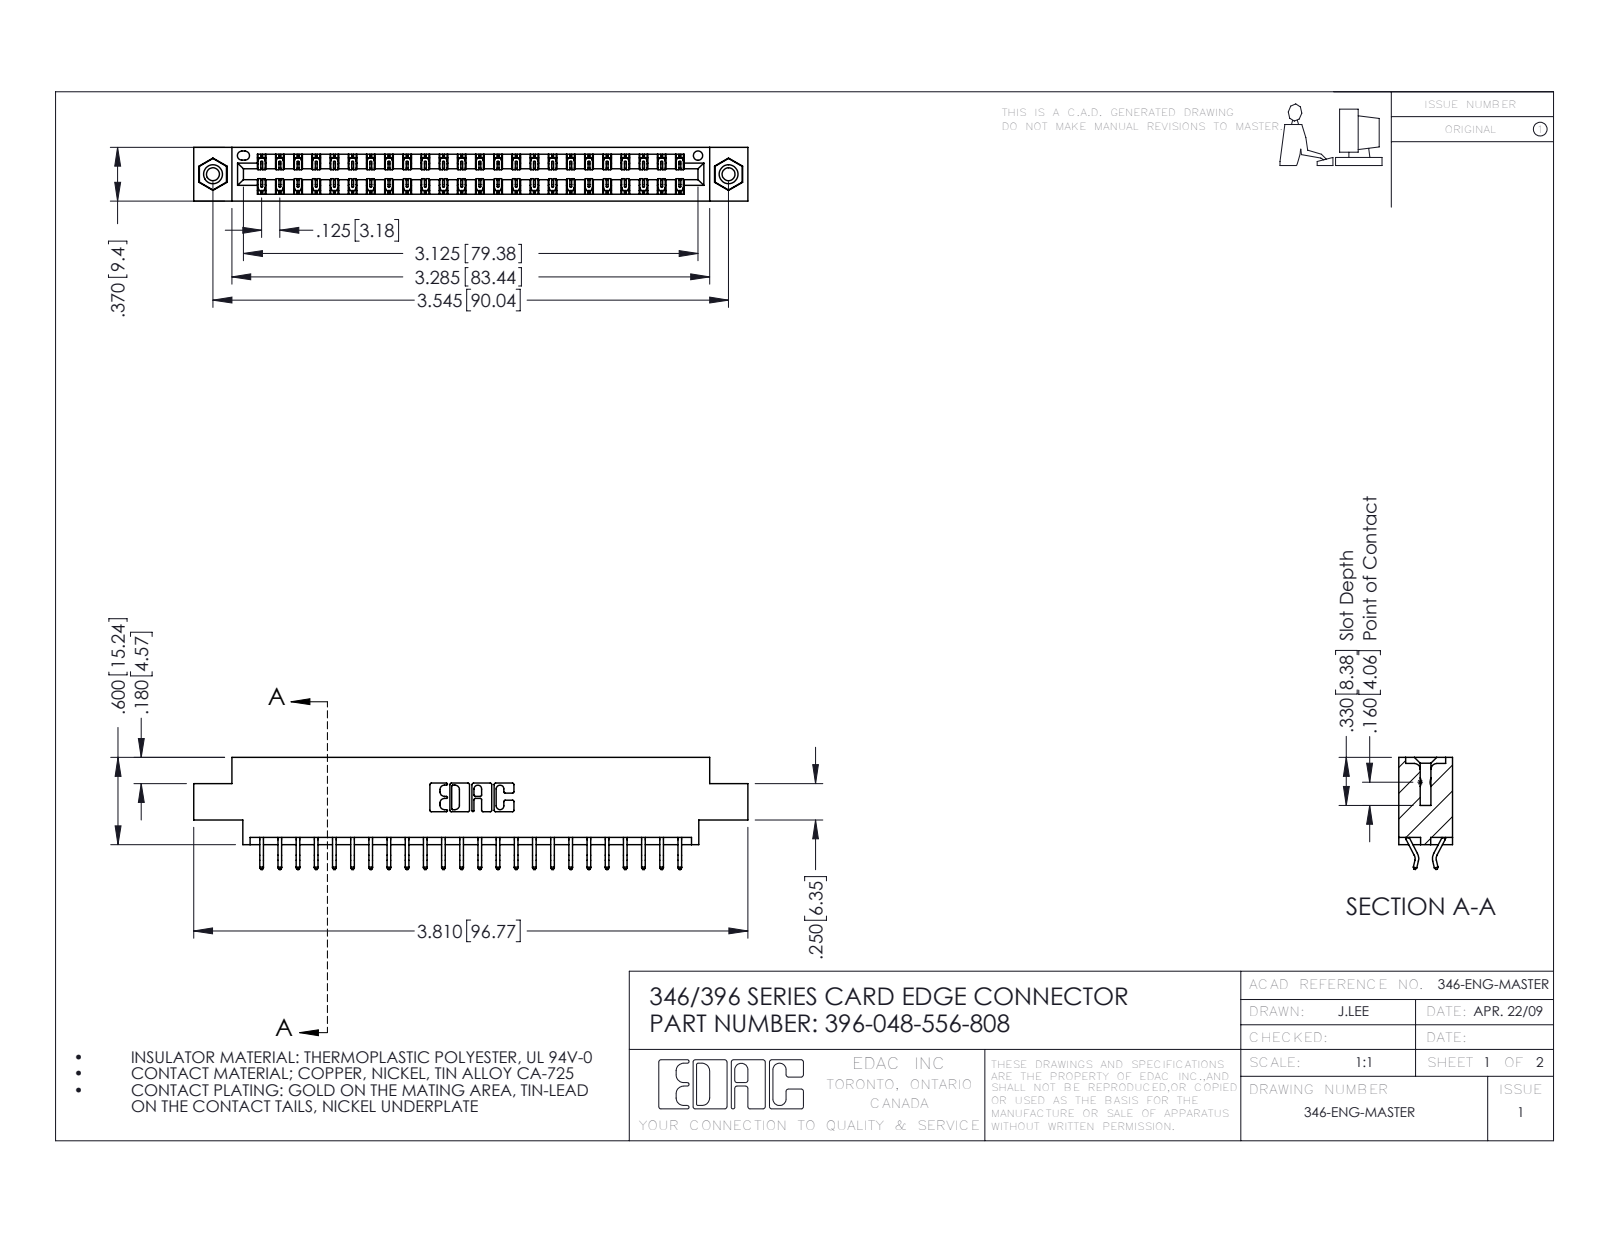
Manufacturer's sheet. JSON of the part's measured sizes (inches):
{"part_name": "345-250-001_345-250-003-102; 345-292-001_556 Tail; 396-048-556-808; 346 Part_0.170 Offset - 0.156 Dia-TI", "step_written_by": "SolidWorks 2016 (CONFIG_CONTROL_DESIGN)", "units": "inches", "bodies": {"solids": 51, "faces": 2970, "planar": 1984, "cylindrical": 970, "other": 16}, "overall_size": [3.81, 0.77, 0.37], "volume_in3": 0.557, "surface_area_in2": 19.26, "round_holes": [[0.089, 2], [0.125, 2], [0.156, 2], [0.064, 1]], "round_bosses_or_shafts": [[0.155, 2]], "partial_cylinders_radius": [[0.006, 72], [0.01, 22], [0.007, 6], [0.031, 6], [0.026, 3], [0.01, 2], [0.014, 2], [0.022, 2]], "face_to_face_distances": [0.048, 0.322, 0.37, 0.25, 0.025, 0.072, 0.298, 0.275, 0.222, 0.148], "hole_center_spacings": [0.246, 3.337, 3.545]}
